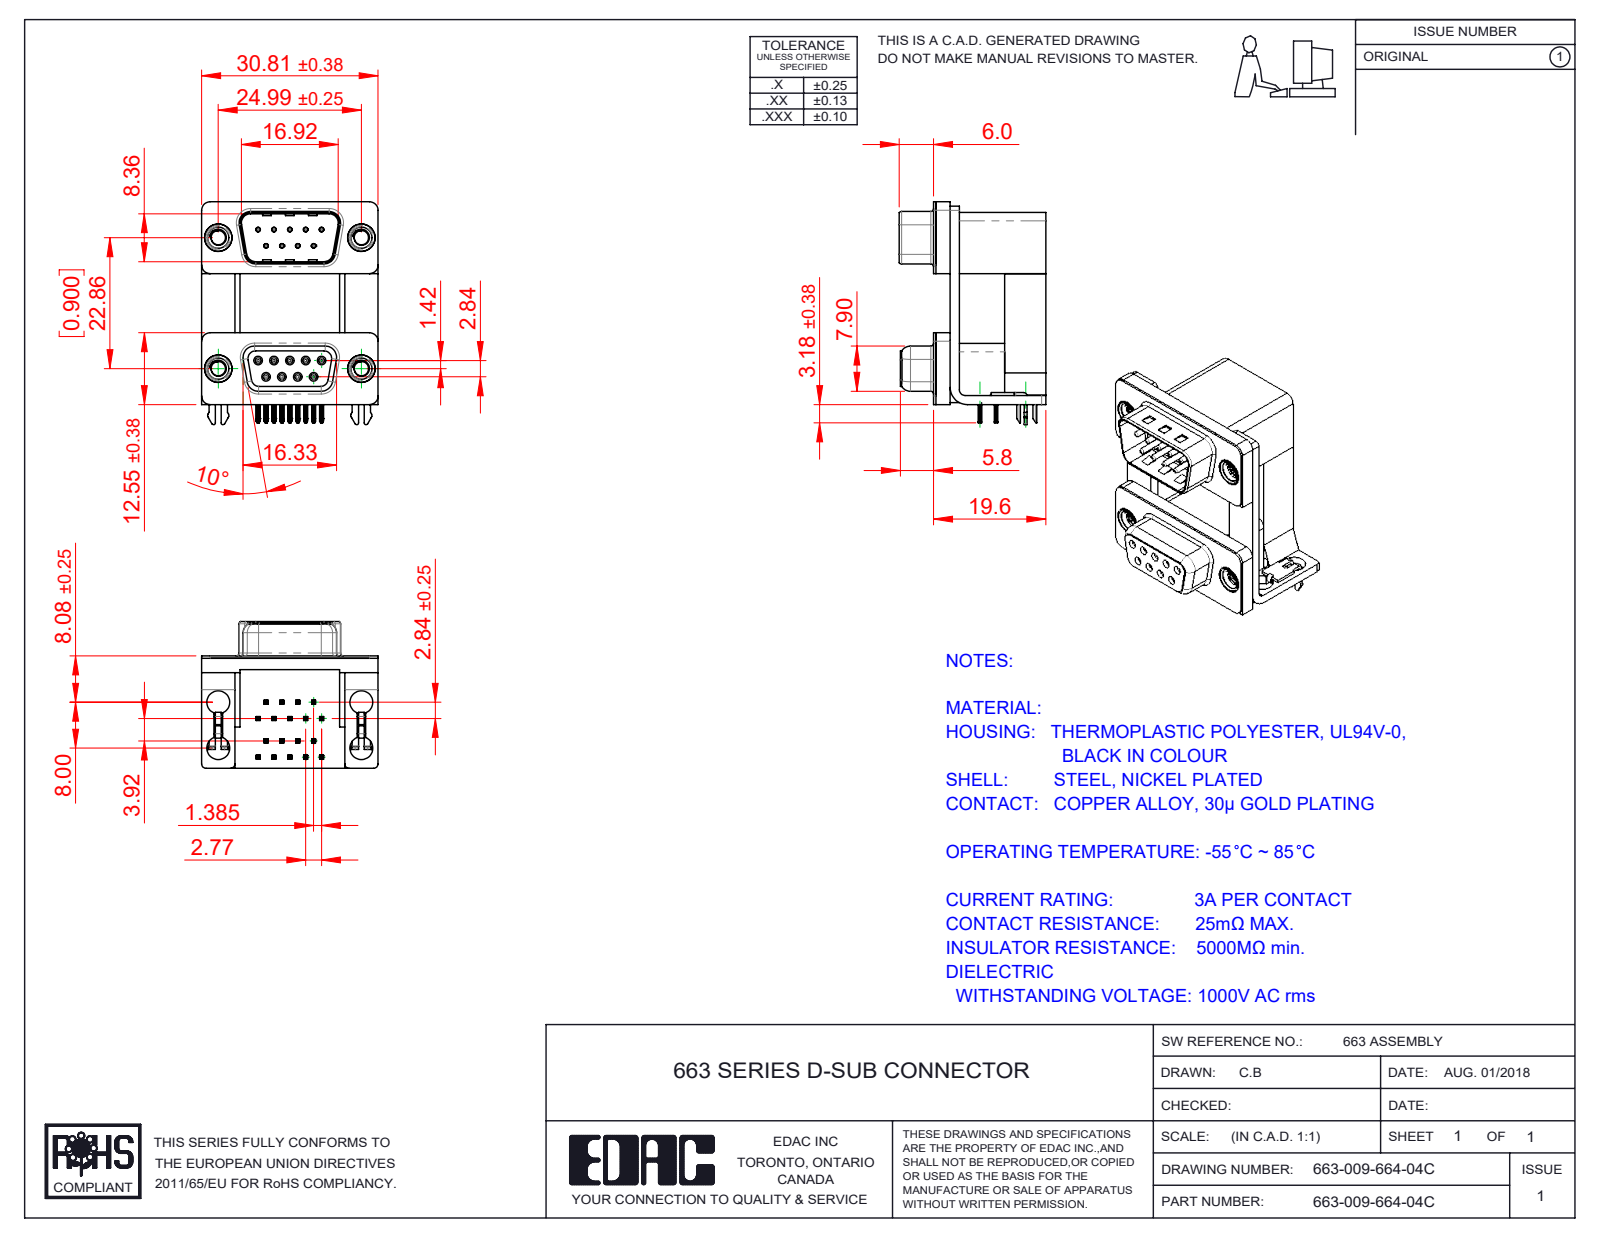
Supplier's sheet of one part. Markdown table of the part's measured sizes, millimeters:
| quantity | value |
| --- | --- |
| part name | 663 Shell Receptacle_09 Contacts; 663 Shell Plug_09 Contacts; 663-009-664-04C; 663 Contact Bottom Upper_H (+8 more) |
| STEP written by | SolidWorks 2020 (CONFIG_CONTROL_DESIGN) |
| units | millimeters |
| bodies | 31 solids, 2641 faces (1341 planar, 733 cylindrical, 567 other) |
| overall size | 38.91 × 30.81 × 25.6 |
| volume | 11 336 mm³ |
| surface area | 13 162 mm² |
| round holes (diameter × count) | 0.8 × 18, 0.35 × 9, 0.9 × 9, 4 × 8, 2.5 × 4, 3.5 × 4, 4.8 × 4, 5 × 4 |
| round bosses / shafts (diameter × count) | 1.2 × 9, 0.75 × 9, 4.9 × 4, 4.75 × 4, 3.9 × 4 |
| partial cylindrical surfaces (radius × count) | 0.1 × 73, 0.25 × 42, 0.15 × 36, 0.12 × 18, 0.35 × 18, 0.5 × 16, 1.5 × 15, 0.75 × 10 |
| main face-to-face distances | 2.5, 0.4, 19.2, 16.7, 12, 7.2, 9.5, 1.6, 12.4, 19.6 |
| hole center spacings | 3.16, 2.77, 23.03, 22.86, 5.54, 23.52, 20.07, 25.74 |
